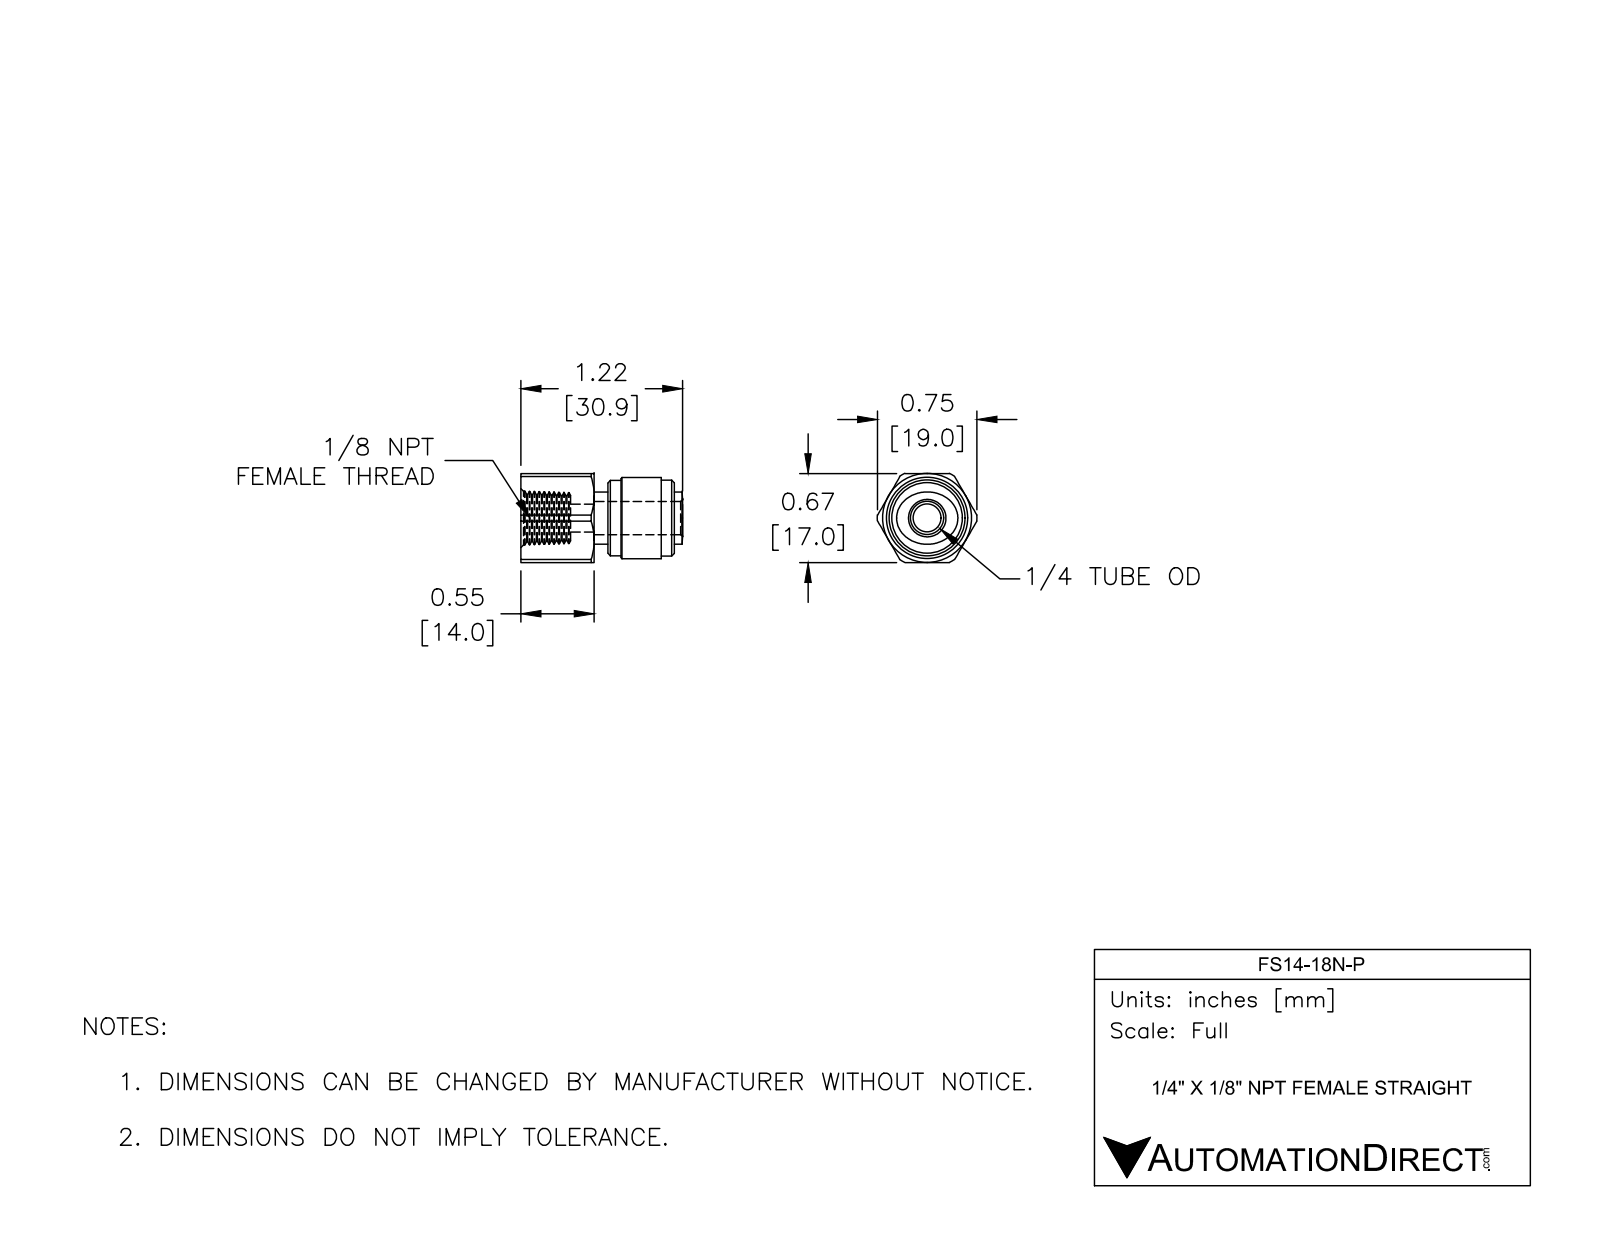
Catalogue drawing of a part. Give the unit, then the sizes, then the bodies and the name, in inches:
Units: inches
Overall size (bounding box): 1.217 × 0.748 × 0.669
Round holes (diameter × count): ⌀0.209 ×1, ⌀0.25 ×1
Round bosses / shafts (diameter × count): ⌀0.61 ×1, ⌀0.571 ×1, ⌀0.567 ×1, ⌀0.394 ×1
Partial cylindrical surfaces — rounded edges, fillets, slot ends (radius × count): R0.374 ×1
Main face-to-face distances: 0.669, 0.551, 0.654, 0.102, 1.154, 0.602, 0.5, 0.098, 0.402, 0.374
Volume: 0.293 in³ · Surface area: 4.696 in²
Bodies: 1 solid, 148 faces (14 planar, 18 cylindrical, 116 other)
Part name (STEP PRODUCT): FS14-18N-P
STEP written by: SolidWorks 2017 (AUTOMOTIVE_DESIGN)
